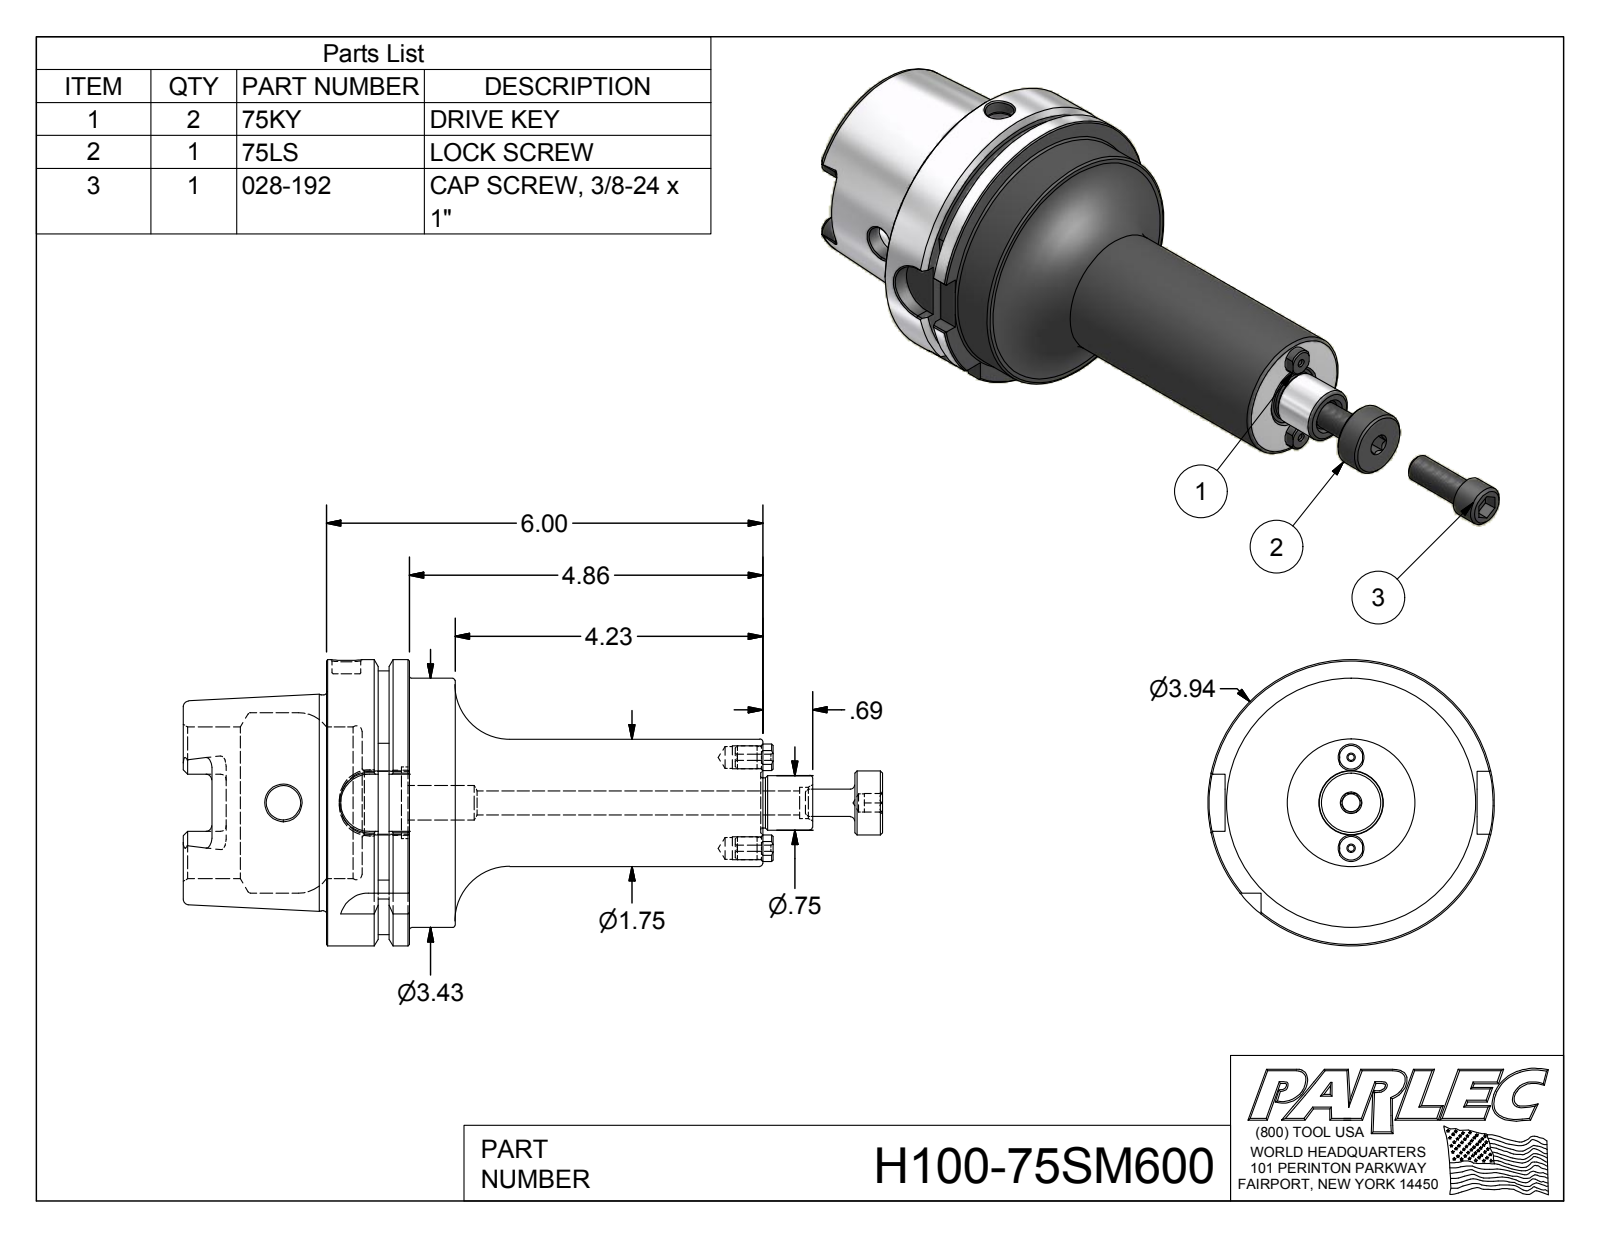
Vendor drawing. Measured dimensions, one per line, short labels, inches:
name: H100-75SM600; 75KY; 75LS; 028-192
written by: Autodesk Inventor 2012 (AUTOMOTIVE_DESIGN)
unit: in
bodies: 5 solids, 225 faces (83 planar, 62 cylindrical, 80 other)
size: 11.717 × 3.937 × 3.937
volume: 32.44 in³; area: 121.8 in²
holes: 2× ⌀0.084, 2× ⌀0.3, 2× ⌀0.312, 2× ⌀0.472, 1× ⌀0.25, 1× ⌀0.33, 1× ⌀0.394, 1× ⌀0.43, 1× ⌀0.881, 1× ⌀0.985, 1× ⌀2.087, 1× ⌀2.48
bosses: 2× ⌀0.318, 1× ⌀3.937, 1× ⌀3.425, 1× ⌀2.967, 1× ⌀1.75, 1× ⌀0.88, 1× ⌀0.75, 1× ⌀0.69
rounds: 6× R0.079, 4× R0.192, 4× R0.394, 2× R0.183, 1× R1.811
face distances: 0.65, 0.492, 1.142, 6, 5.508, 4.858, 1.969, 2.461, 3.11, 7.969
hole spacings: 0.625, 0.625, 1.25, 1.25
